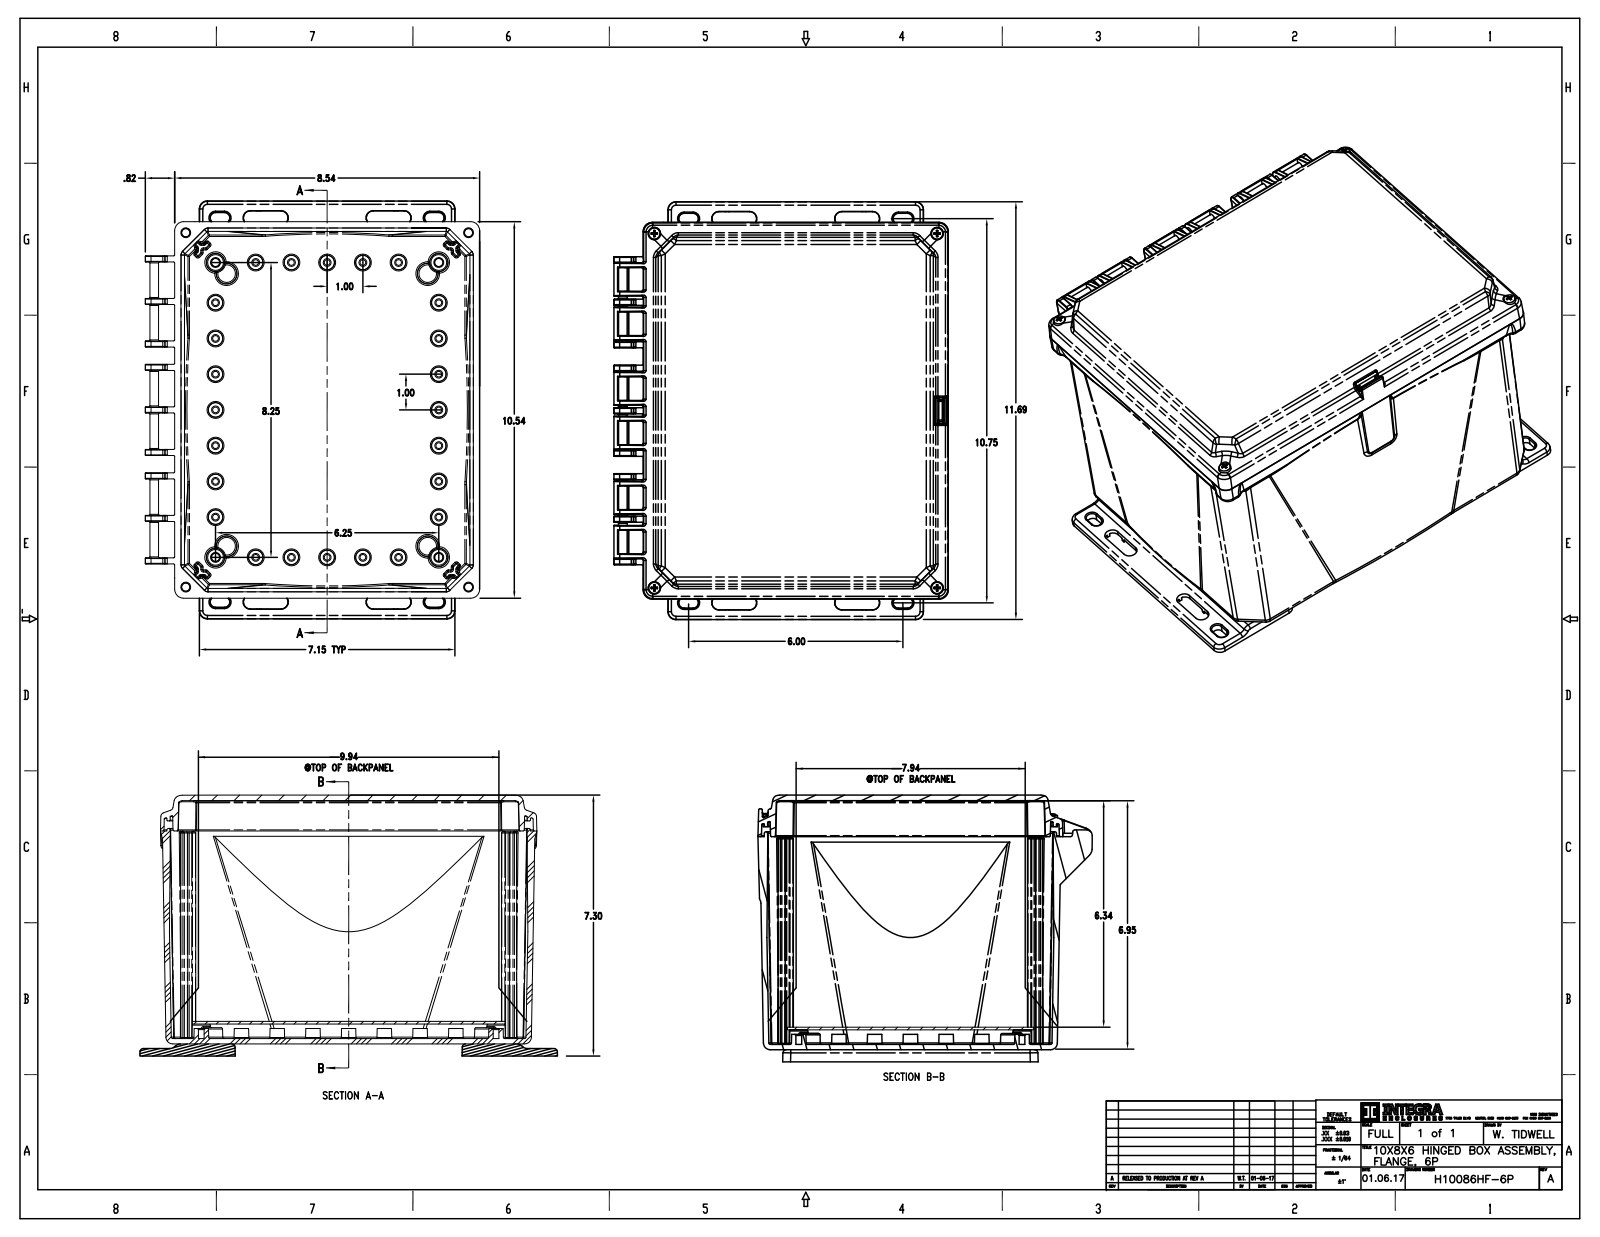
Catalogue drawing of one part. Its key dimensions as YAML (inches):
part_name: "H1086BH; 9912525-80-10; 9912521-80-10; H1086BH_ASM (+5 more)"
step_written_by: "CREO PARAMETRIC BY PTC INC, 2016050 (CONFIG_CONTROL_DESIGN)"
units: inches
bodies: {solids: 24, faces: 4448, planar: 1087, cylindrical: 1793, other: 1568}
overall_size: [11.69, 9.359, 7.655]
volume: 77.16
surface_area: 1059
round_holes:
  - {diameter: 0.16, count: 24}
  - {diameter: 0.19, count: 8}
  - {diameter: 0.201, count: 4}
round_bosses_or_shafts:
  - {diameter: 0.25, count: 12}
  - {diameter: 0.3, count: 8}
  - {diameter: 0.298, count: 8}
  - {diameter: 0.29, count: 8}
  - {diameter: 0.26, count: 8}
  - {diameter: 0.258, count: 8}
  - {diameter: 0.375, count: 4}
  - {diameter: 0.372, count: 4}
partial_cylinders:
  - {radius: 0.03, count: 364}
  - {radius: 0.02, count: 179}
  - {radius: 0.015, count: 90}
  - {radius: 0.005, count: 49}
  - {radius: 0.09, count: 44}
  - {radius: 0.01, count: 43}
  - {radius: 0.04, count: 36}
  - {radius: 0.1, count: 28}
face_to_face_distances: [0.15, 0.19, 0.49, 0.34, 0.12, 5.81, 5.96, 0.392, 0.13, 0.098]
hole_center_spacings: [1, 2, 3, 6.33, 6.563, 2.128, 2.404, 3.073]
